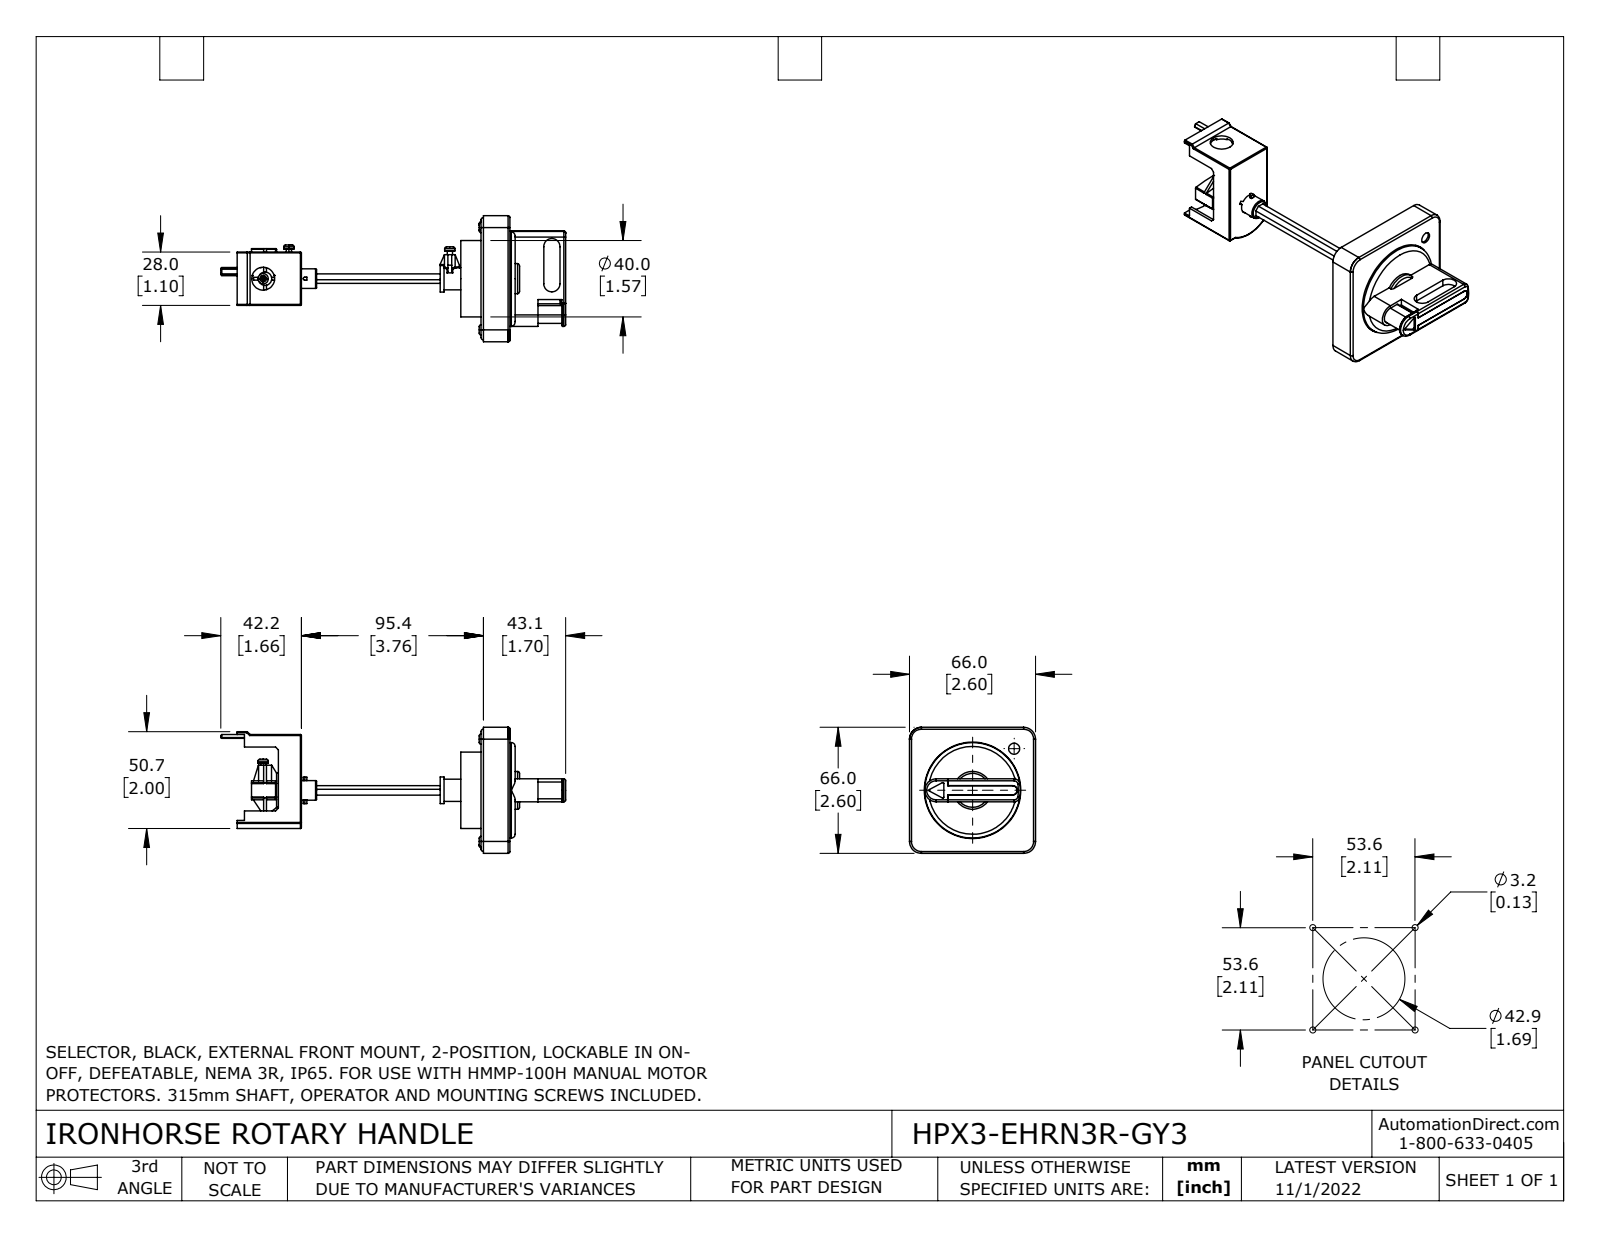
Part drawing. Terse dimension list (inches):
name: HPX3-EHRN3R-GY3
written by: SolidWorks 2021 (CONFIG_CONTROL_DESIGN)
unit: in
bodies: 5 solids, 776 faces (444 planar, 226 cylindrical, 106 other)
size: 7.114 × 2.598 × 2.598
volume: 6.296 in³; area: 60.53 in²
holes: 2× ⌀0.11, 1× ⌀0.126, 1× ⌀0.228, 1× ⌀0.252, 1× ⌀0.406, 1× ⌀0.417, 1× ⌀0.472, 1× ⌀1.988
bosses: 7× ⌀0.213, 3× ⌀0.109, 1× ⌀1.969, 1× ⌀1.575, 1× ⌀1.307, 1× ⌀0.709, 1× ⌀0.551, 1× ⌀0.461
rounds: 30× R0.02, 28× R0.008, 10× R0.039, 5× R0.138, 4× R0.012, 4× R0.052, 4× R0.118, 4× R0.244
face distances: 0.059, 0.547, 1.398, 1.201, 1.063, 0.654, 2.598, 1.535, 3.756, 4.303
hole spacings: 0.039, 0.772, 1.214, 1.842
